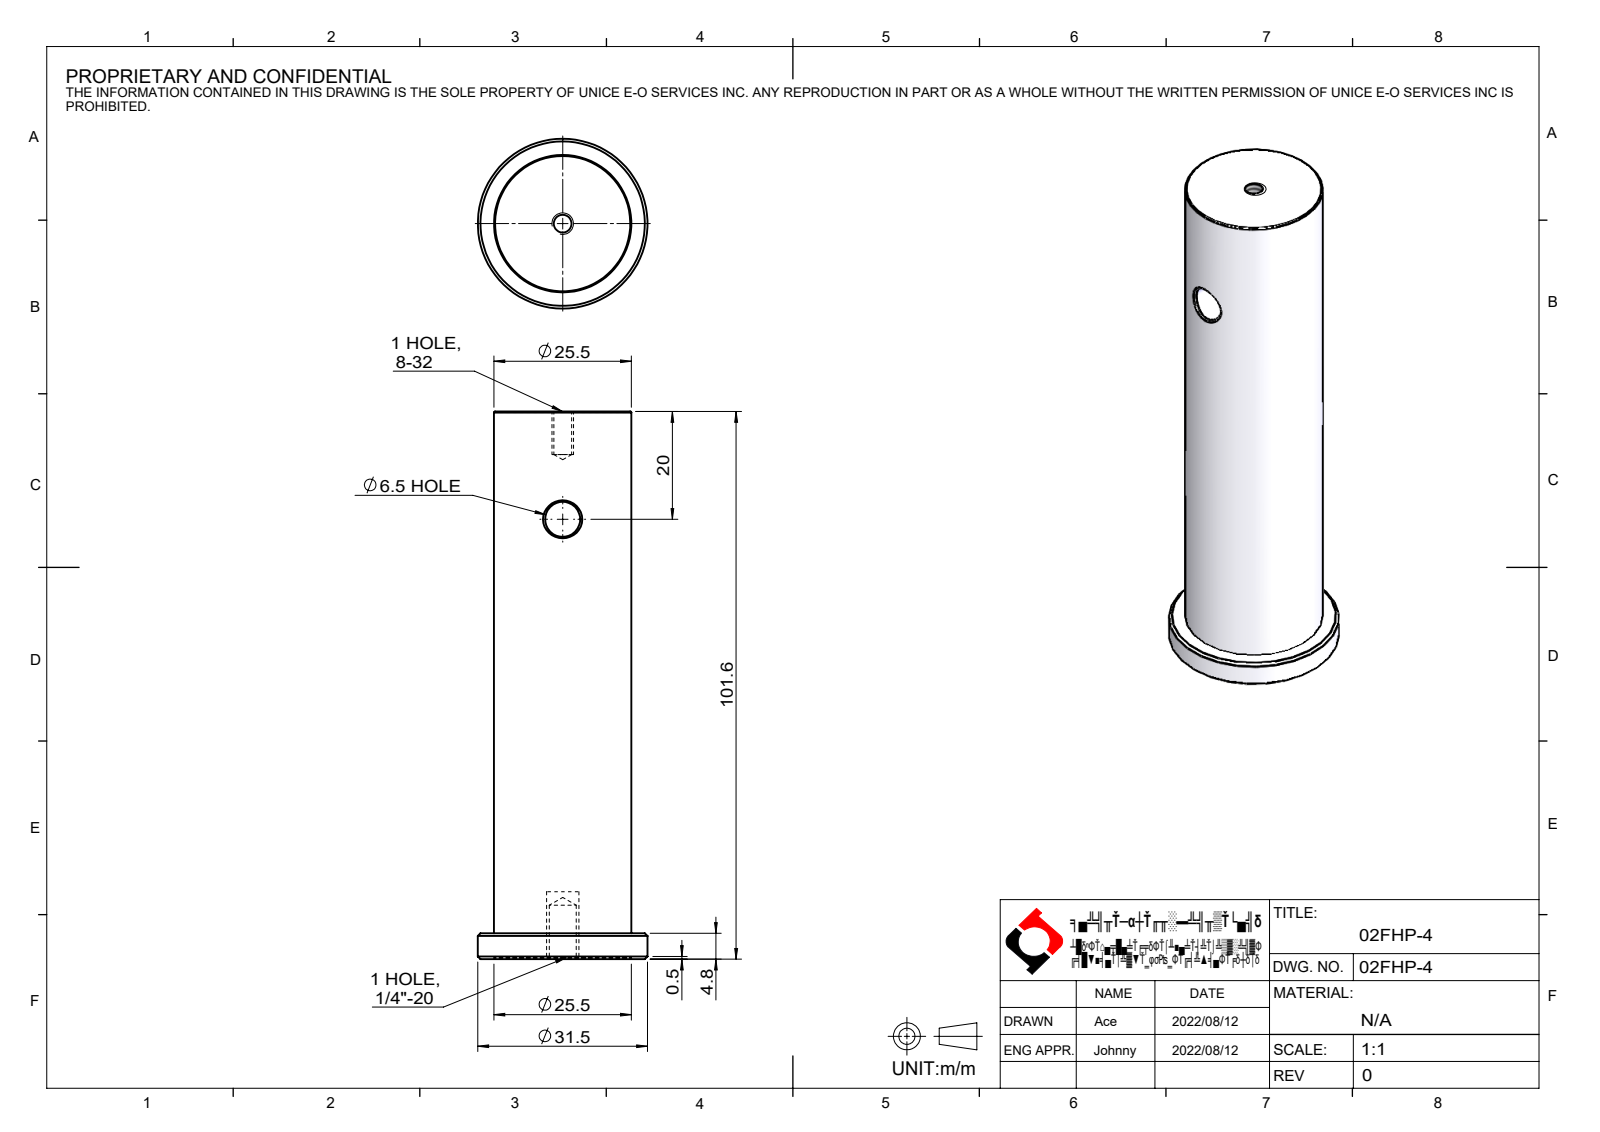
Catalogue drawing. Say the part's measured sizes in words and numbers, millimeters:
The part is named "02FHP-4". Its 3-D file was written by "SolidWorks 2020 (CONFIG_CONTROL_DESIGN)". It is 1 solid with 34 faces: 4 planar, 12 cylindrical and 18 other. Overall it measures 101.6 by 31.5 by 31.5 millimeters. Its volume is 51 788 cubic millimeters and its surface area 10 424 square millimeters. Round holes: 1 of diameter 3.3, 1 of diameter 5, 1 of diameter 6.5, 1 of diameter 25.5. Round bosses or shafts: 1 of diameter 31.5. The main face-to-face distances are 101.1, 4.3, 96.8, 0.5, 4.8, 101.6.
